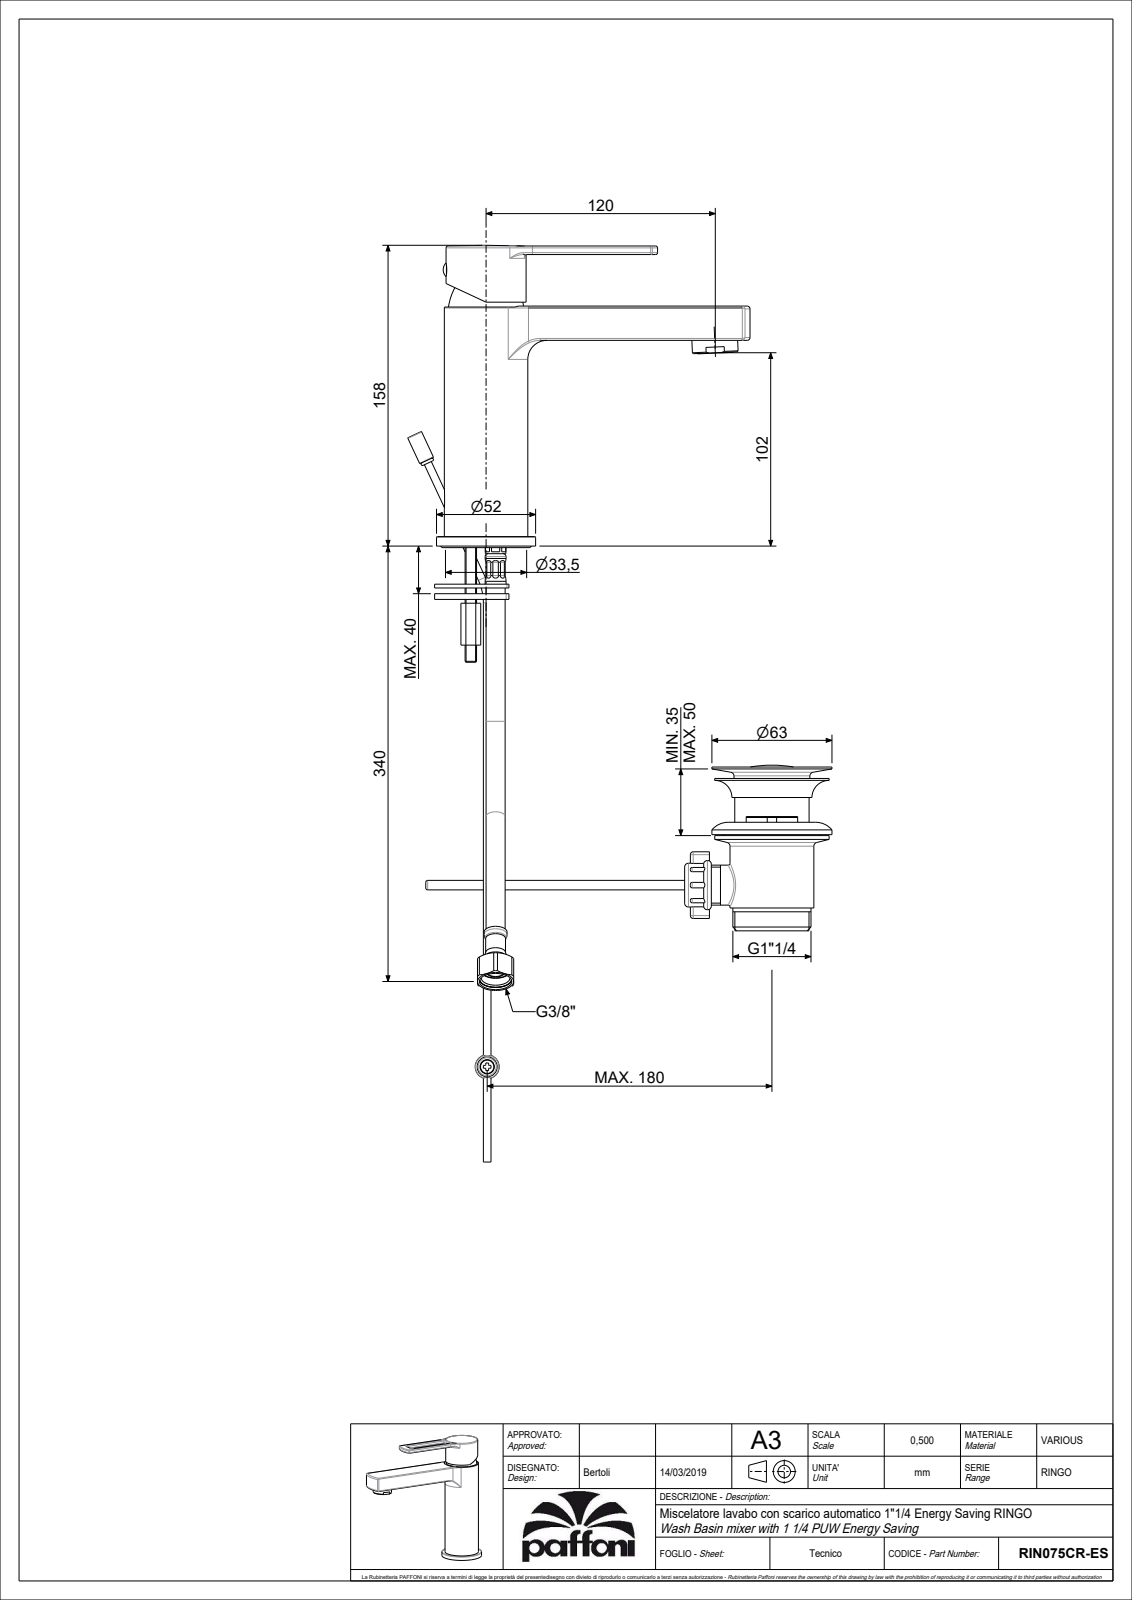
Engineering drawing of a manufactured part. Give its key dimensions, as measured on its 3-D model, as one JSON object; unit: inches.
{"part_name": "RIN075CR", "step_written_by": "CREO PARAMETRIC BY PTC INC, 2020044 (CONFIG_CONTROL_DESIGN)", "units": "inches", "bodies": {"solids": 3, "faces": 271, "planar": 60, "cylindrical": 80, "other": 131}, "overall_size": [7.397, 6.257, 2.047], "volume_in3": 16.98, "surface_area_in2": 74.3, "round_holes": [[0.118, 1], [0.307, 1]], "round_bosses_or_shafts": [[2.047, 1], [1.685, 1], [1.654, 1], [0.945, 1], [0.315, 1], [0.299, 1], [0.217, 1], [0.197, 1]], "partial_cylinders_radius": [[0.039, 14], [0.02, 12], [0.079, 4], [0.787, 2], [0.807, 2], [1.168, 1], [1.616, 1]], "face_to_face_distances": [0.669, 4.311, 4.98, 1.181, 0.197, 0.472, 5.453, 1.142, 0.612, 6.065]}
